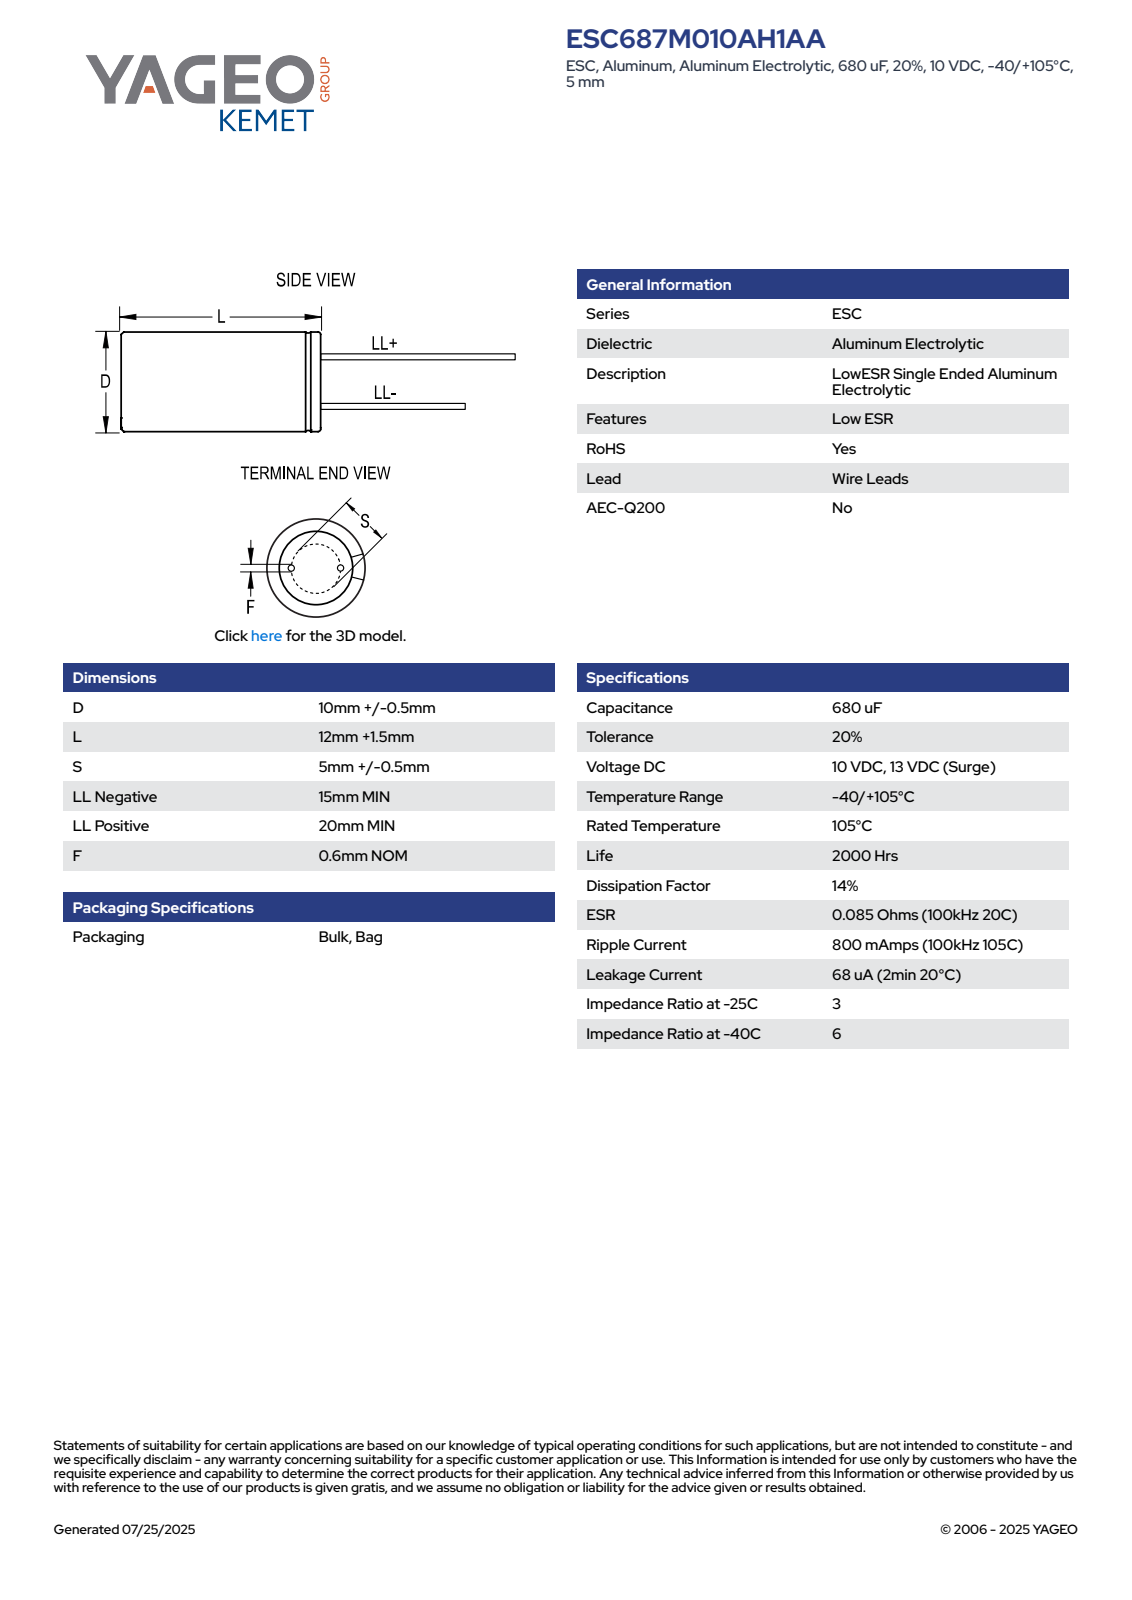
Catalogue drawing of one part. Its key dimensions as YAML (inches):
part_name: "CAR_KLP_10X12_D10.5L13.5S5F0.6"
step_written_by: "SolidWorks 2014 (AUTOMOTIVE_DESIGN)"
units: inches
bodies: {solids: 4, faces: 75, planar: 61, cylindrical: 8, other: 6}
overall_size: [1.319, 0.413, 0.413]
volume: 0.071
surface_area: 1.1
round_bosses_or_shafts:
  - {diameter: 0.024, count: 2}
  - {diameter: 0.413, count: 1}
face_to_face_distances: [0.531, 0.532, 1.122, 1.319, 1.122, 1.319, 0.591, 0.787, 0.197, 0.056]
